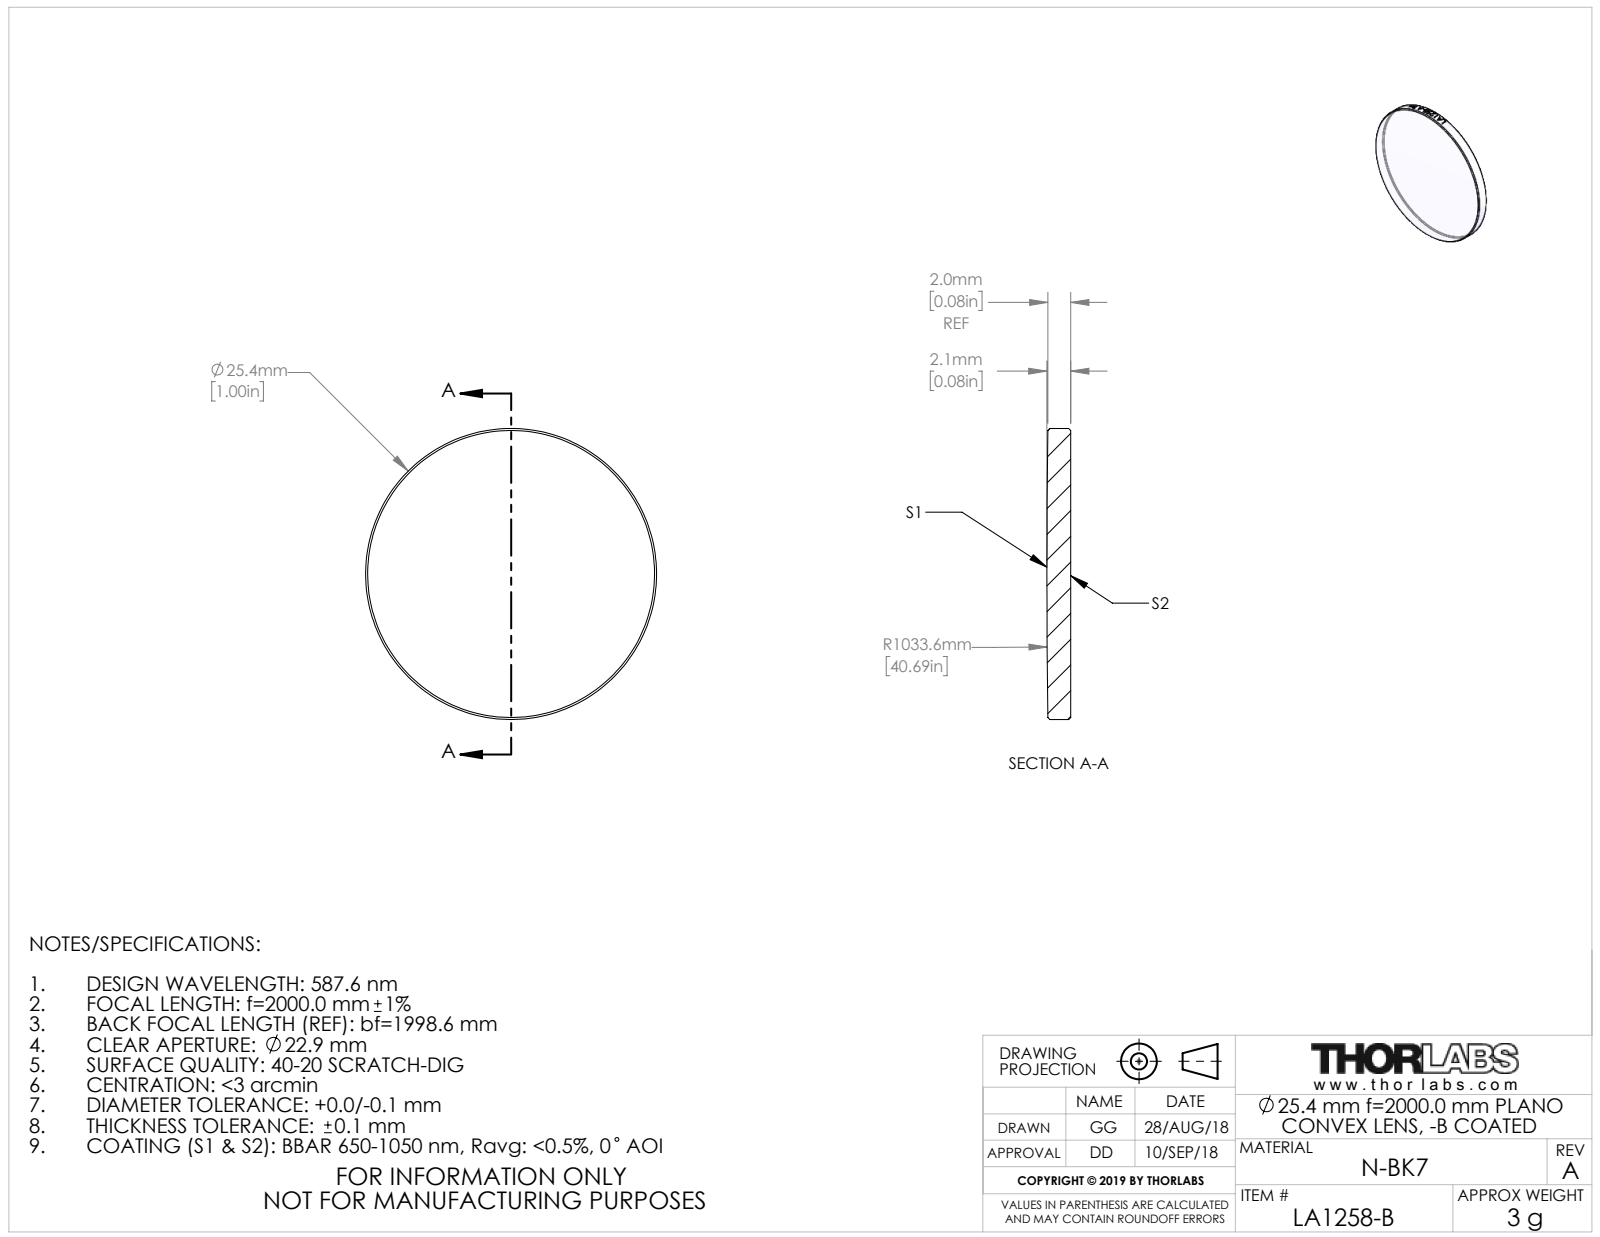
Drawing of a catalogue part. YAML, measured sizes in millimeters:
part_name: "TTN162128-E0W"
step_written_by: "SolidWorks 2018 (CONFIG_CONTROL_DESIGN)"
units: millimeters
bodies: {solids: 1, faces: 28, planar: 1, cylindrical: 21, other: 6}
overall_size: [25.4, 25.4, 2.08]
volume: 1032
surface_area: 1157
round_bosses_or_shafts:
  - {diameter: 25.4, count: 1}
